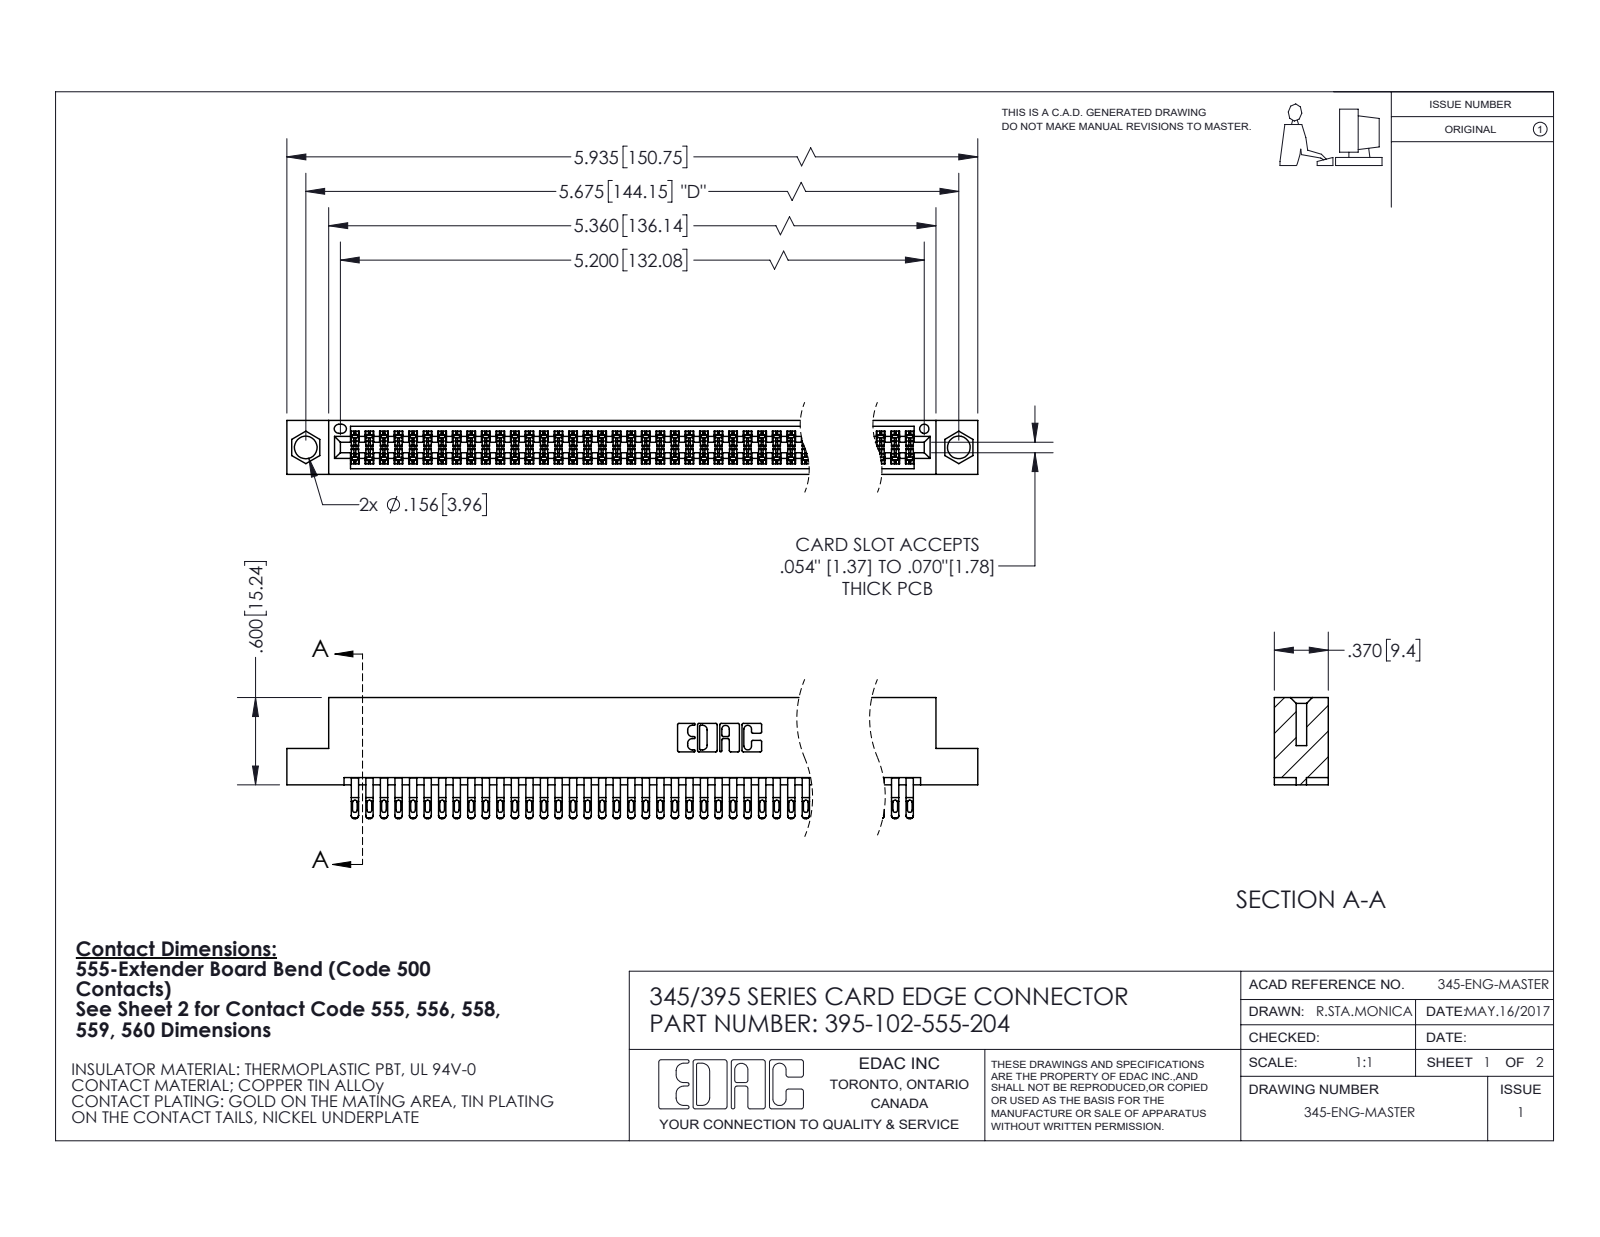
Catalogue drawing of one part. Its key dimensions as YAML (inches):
part_name: "345-292-001_555 Tail; 395-102-555-204; 345 Part_Flush Mounting Lugs - 0.156 Dia-TI"
step_written_by: "SolidWorks 2020 (CONFIG_CONTROL_DESIGN)"
units: inches
bodies: {solids: 103, faces: 5852, planar: 3256, cylindrical: 2596, other: 0}
overall_size: [5.935, 0.832, 0.37]
volume: 0.91
surface_area: 35.81
round_holes:
  - {diameter: 0.156, count: 2}
  - {diameter: 0.064, count: 1}
partial_cylinders:
  - {radius: 0.016, count: 255}
  - {radius: 0.006, count: 204}
  - {radius: 0.02, count: 204}
  - {radius: 0.01, count: 22}
  - {radius: 0.007, count: 6}
  - {radius: 0.031, count: 6}
  - {radius: 0.026, count: 3}
  - {radius: 0.01, count: 2}
face_to_face_distances: [0.298, 0.072, 0.025, 0.37, 0.2, 0.098, 0.272, 0.225, 0.175, 0.149]
hole_center_spacings: [0.27, 5.439, 5.675]
